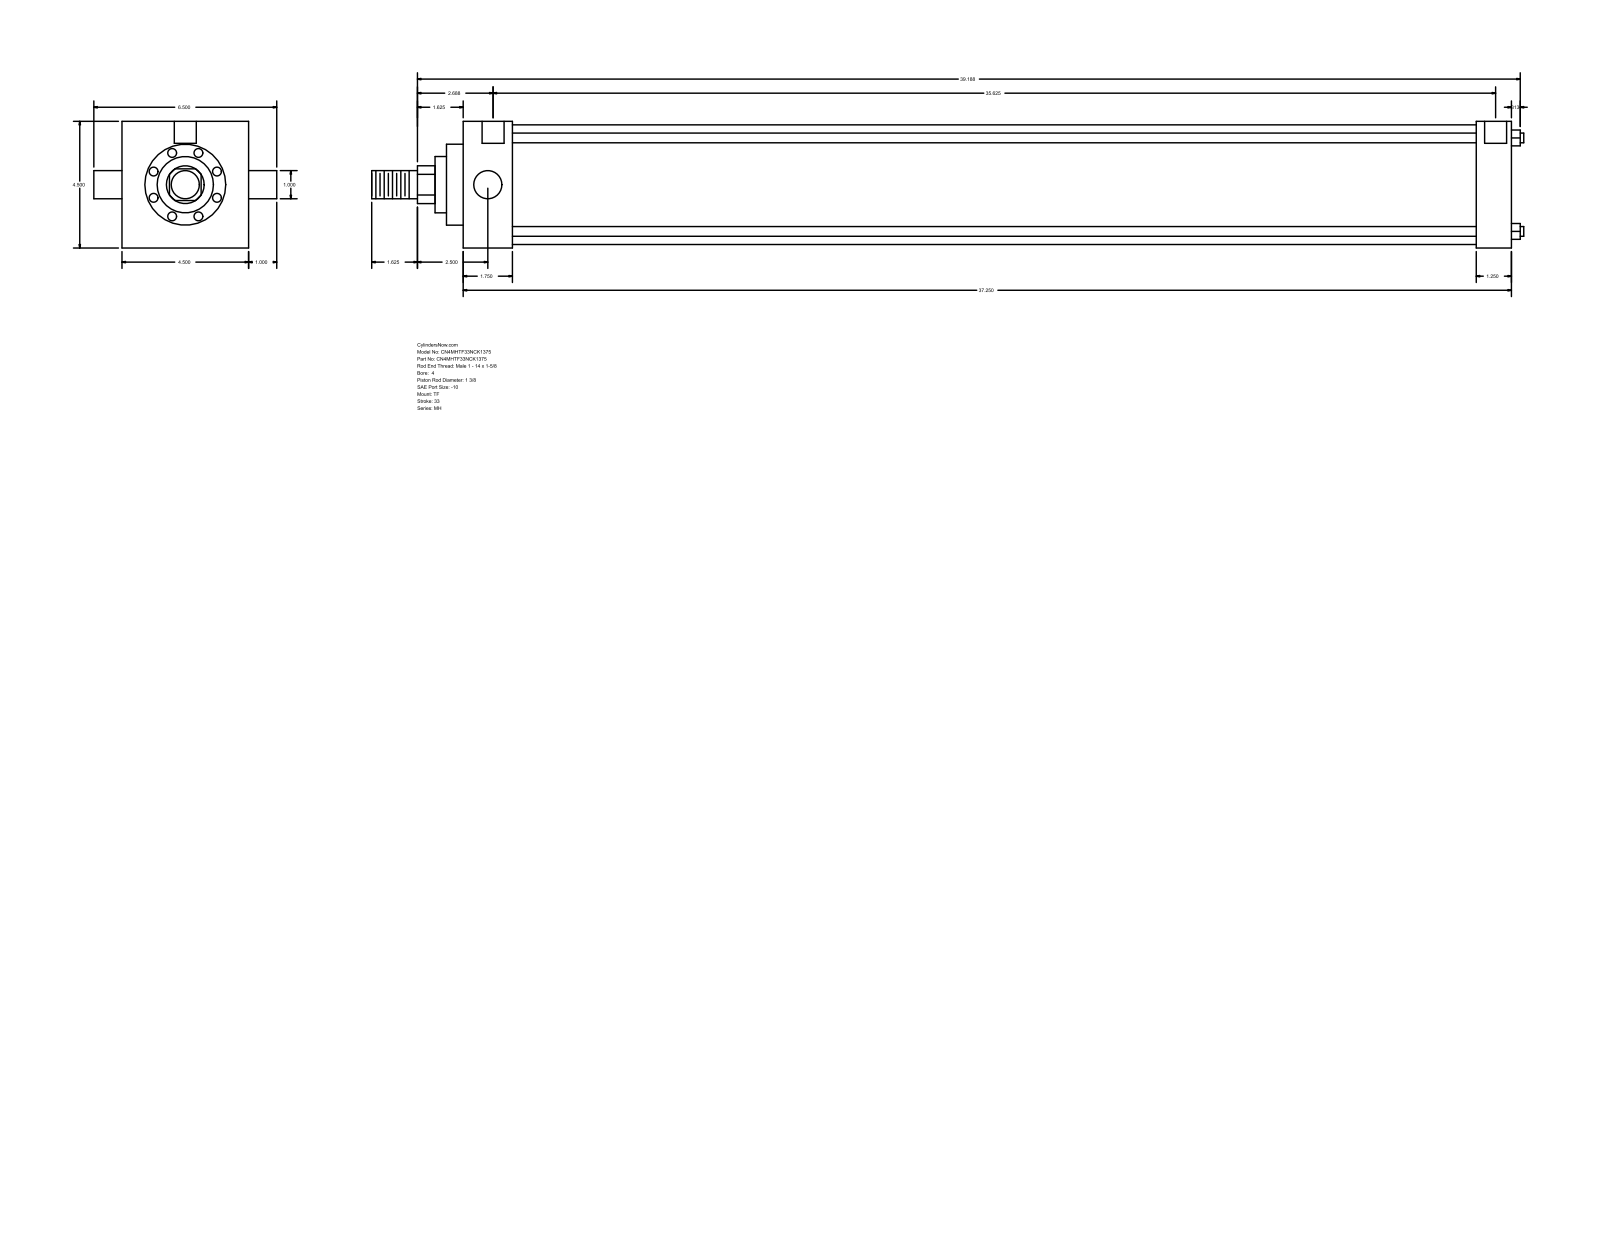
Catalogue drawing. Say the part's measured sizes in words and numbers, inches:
The part is named "MH_TF__0400_1.375". Its 3-D file was written by "GSSL Pune (CONFIG_CONTROL_DESIGN)". It is 0 solids with 86 faces: 61 planar, 25 cylindrical and 0 other. Overall it measures 40.937 by 6.5 by 4.5 inches. Round holes: 3 of diameter 0.344, 2 of diameter 0.781. Round bosses or shafts: 4 of diameter 0.345, 2 of diameter 1, 1 of diameter 4.25, 1 of diameter 2.875, 1 of diameter 2, 1 of diameter 1.375. Partial cylindrical surfaces (rounded edges, fillets, slot ends): 1 of radius 0.672. The main face-to-face distances are 4.5, 37.25, 1.75, 35.5, 36, 34.25, 1.25, 0.594, 2.344, 36.594. The hole center spacings are 0.063, 35.688, 35.625, 35.75.
